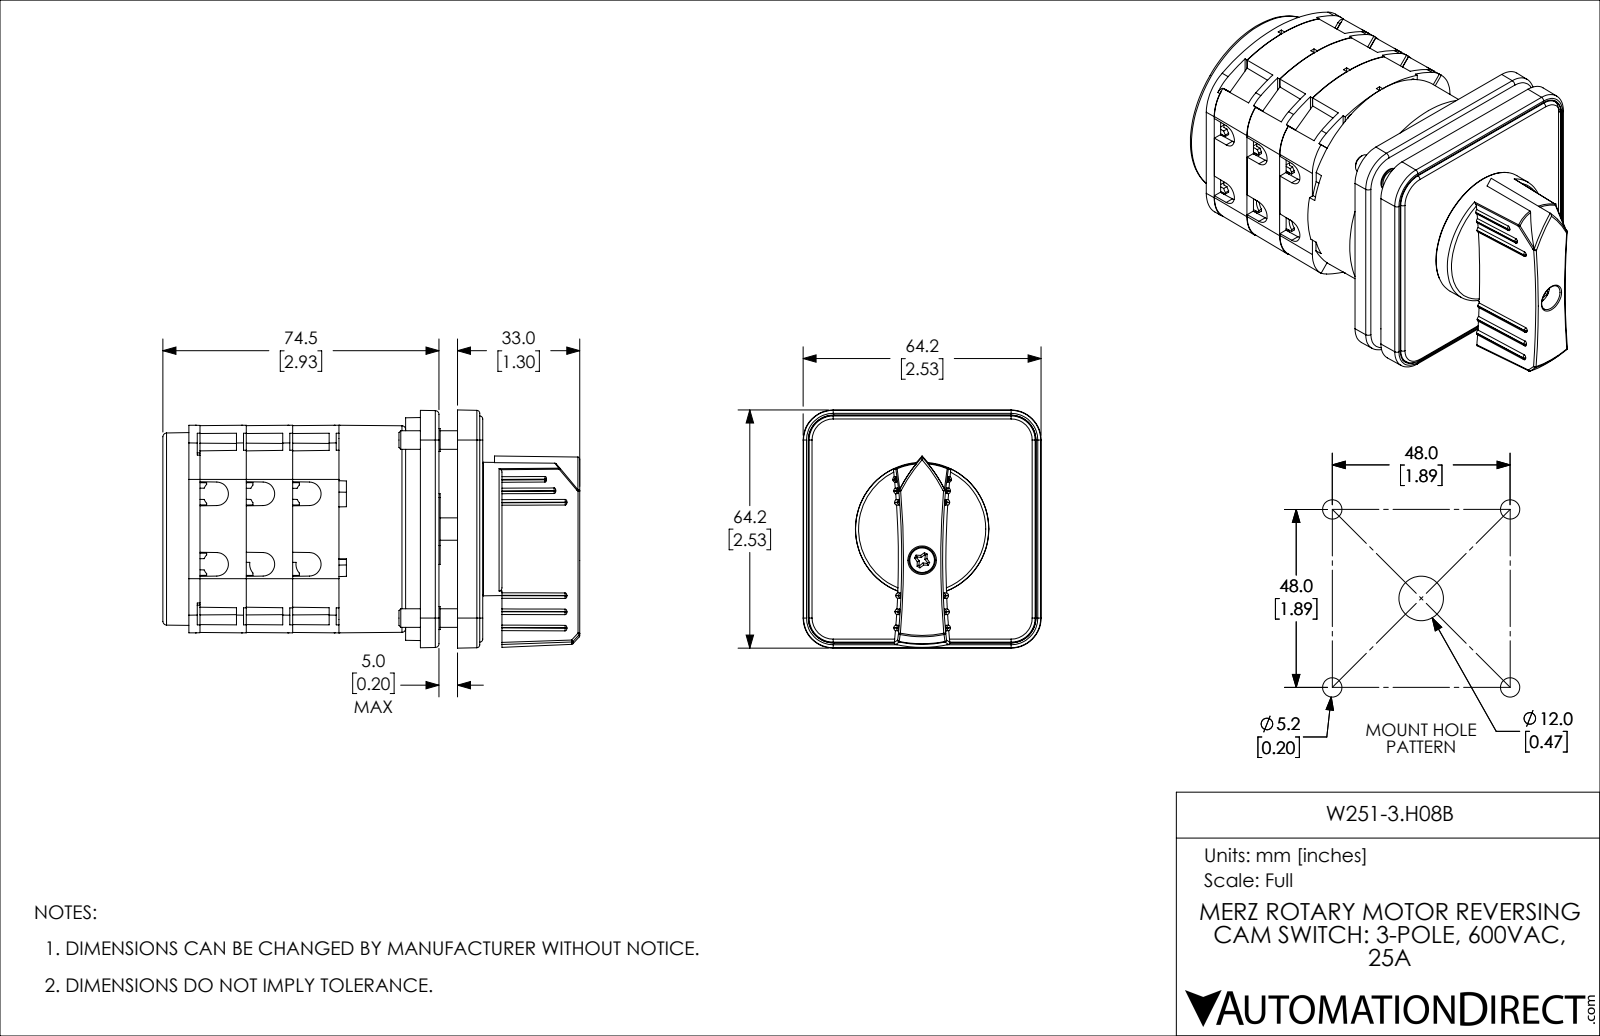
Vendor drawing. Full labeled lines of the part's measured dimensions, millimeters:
Part name (STEP PRODUCT): W251-3.H08B
STEP written by: SolidWorks 2019 (AUTOMOTIVE_DESIGN)
Units: millimetres
Bodies: 13 solids, 3380 faces (2050 planar, 250 cylindrical, 1080 other)
Overall size (bounding box): 112.5 × 64.2 × 64.2
Volume: 192 700 mm³ · Surface area: 96 770 mm²
Round holes (diameter × count): ⌀8 ×6, ⌀0.3 ×4, ⌀4 ×4, ⌀5 ×4, ⌀5.2 ×4, ⌀9.5 ×4, ⌀13 ×1, ⌀14 ×1, ⌀23.5 ×1
Round bosses / shafts (diameter × count): ⌀5 ×5, ⌀9.3 ×4, ⌀8.1 ×4, ⌀7.3 ×4, ⌀15.8 ×1, ⌀10.5 ×1, ⌀7.5 ×1, ⌀3.5 ×1
Partial cylindrical surfaces — rounded edges, fillets, slot ends (radius × count): R0.2 ×14, R0.8 ×11, R0.5 ×6, R3.2 ×6, R3.5 ×6, R1 ×5, R0.2 ×4, R0.5 ×4
Main face-to-face distances: 12.5, 10, 1.8, 11.8, 25, 19, 5, 9, 20.8, 0.8
Hole centre spacings: 42.4, 8.5, 9, 9.3, 9.5, 16.4, 16.5, 18.1
